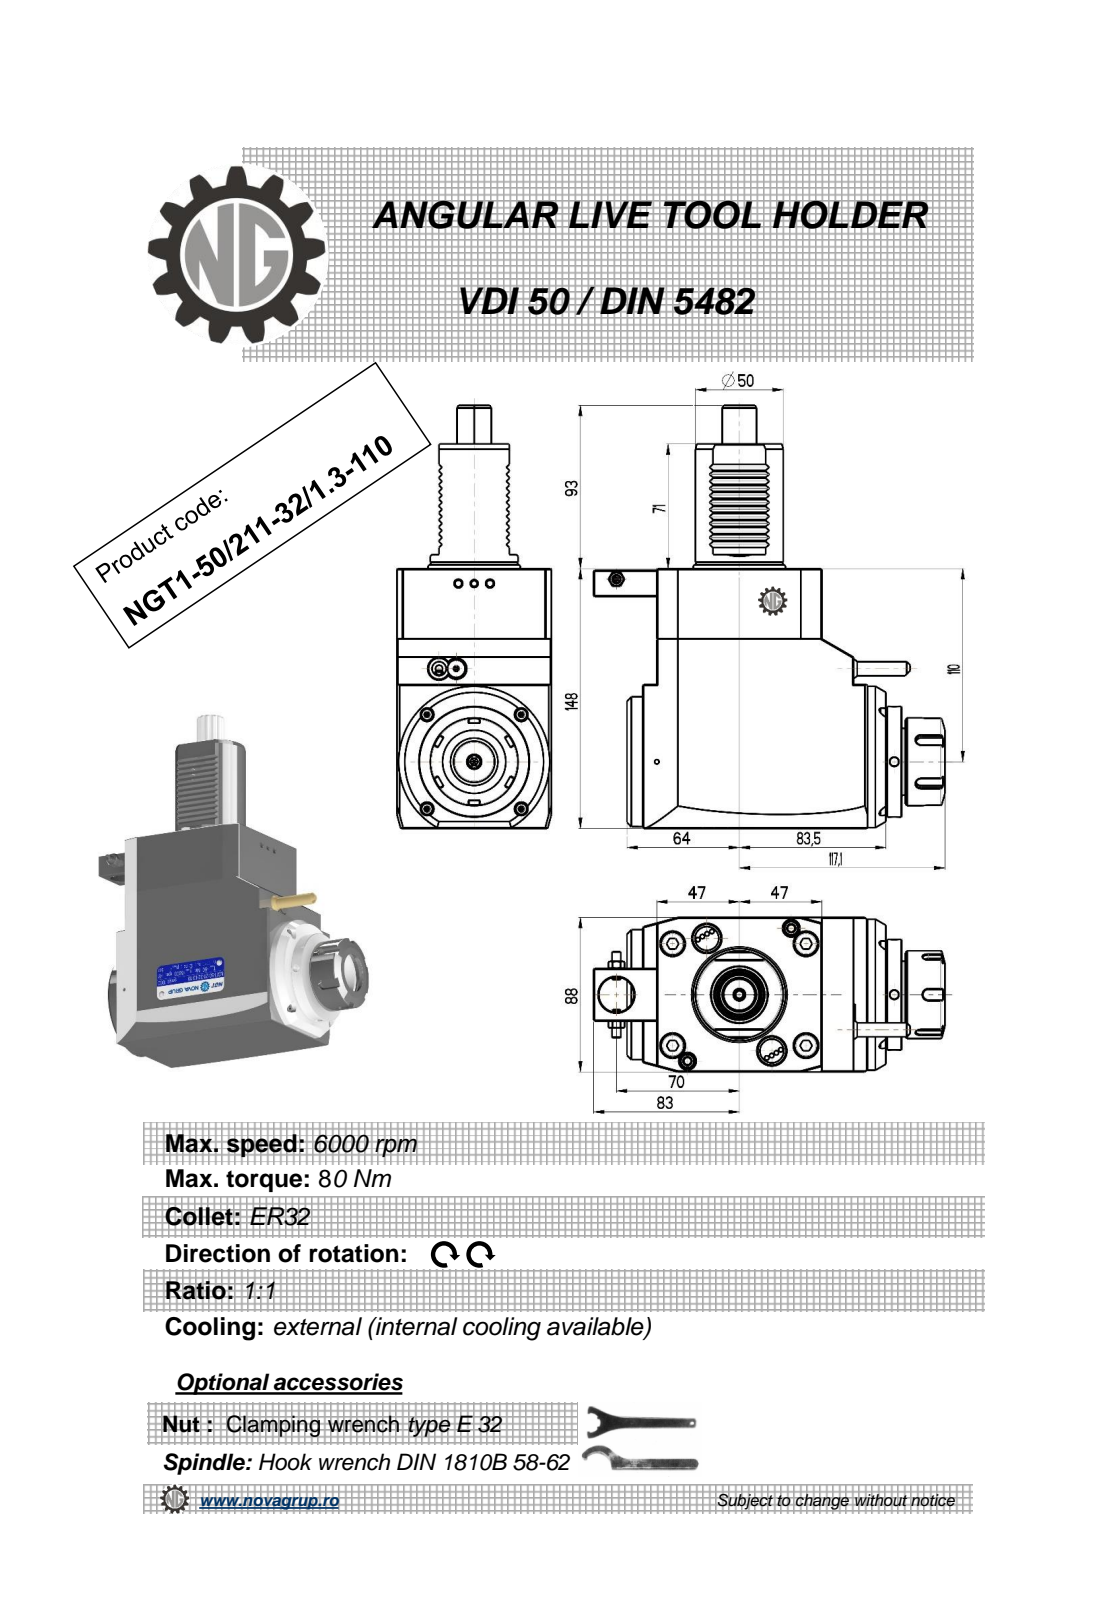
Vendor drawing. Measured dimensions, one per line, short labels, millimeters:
name: NGT1_50_211_32_1_3_110
written by: PRO/ENGINEER BY PARAMETRIC TECHNOLOGY CORPORATION, 2010280 (CONFIG_CONTROL_DESIGN)
unit: mm
bodies: 1 solid, 532 faces (231 planar, 153 cylindrical, 148 other)
size: 241 × 200.1 × 88
volume: 1 792 000 mm³; area: 112 845 mm²
holes: 3× ⌀5, 1× ⌀3, 1× ⌀4.2, 1× ⌀5.3, 1× ⌀9.5, 1× ⌀20, 1× ⌀27
bosses: 2× ⌀50, 1× ⌀86, 1× ⌀74, 1× ⌀63, 1× ⌀41, 1× ⌀10, 1× ⌀8.96, 1× ⌀8
rounds: 24× R0.3, 24× R3.33, 12× R0.26, 6× R0.2, 5× R3, 1× R2.5, 1× R8.25, 1× R9.75
face distances: 88, 148, 147.5, 9, 17, 8, 94, 111, 130.5, 36.5
hole spacings: 52.46, 56.65, 70, 88.25, 101.5, 158.25
